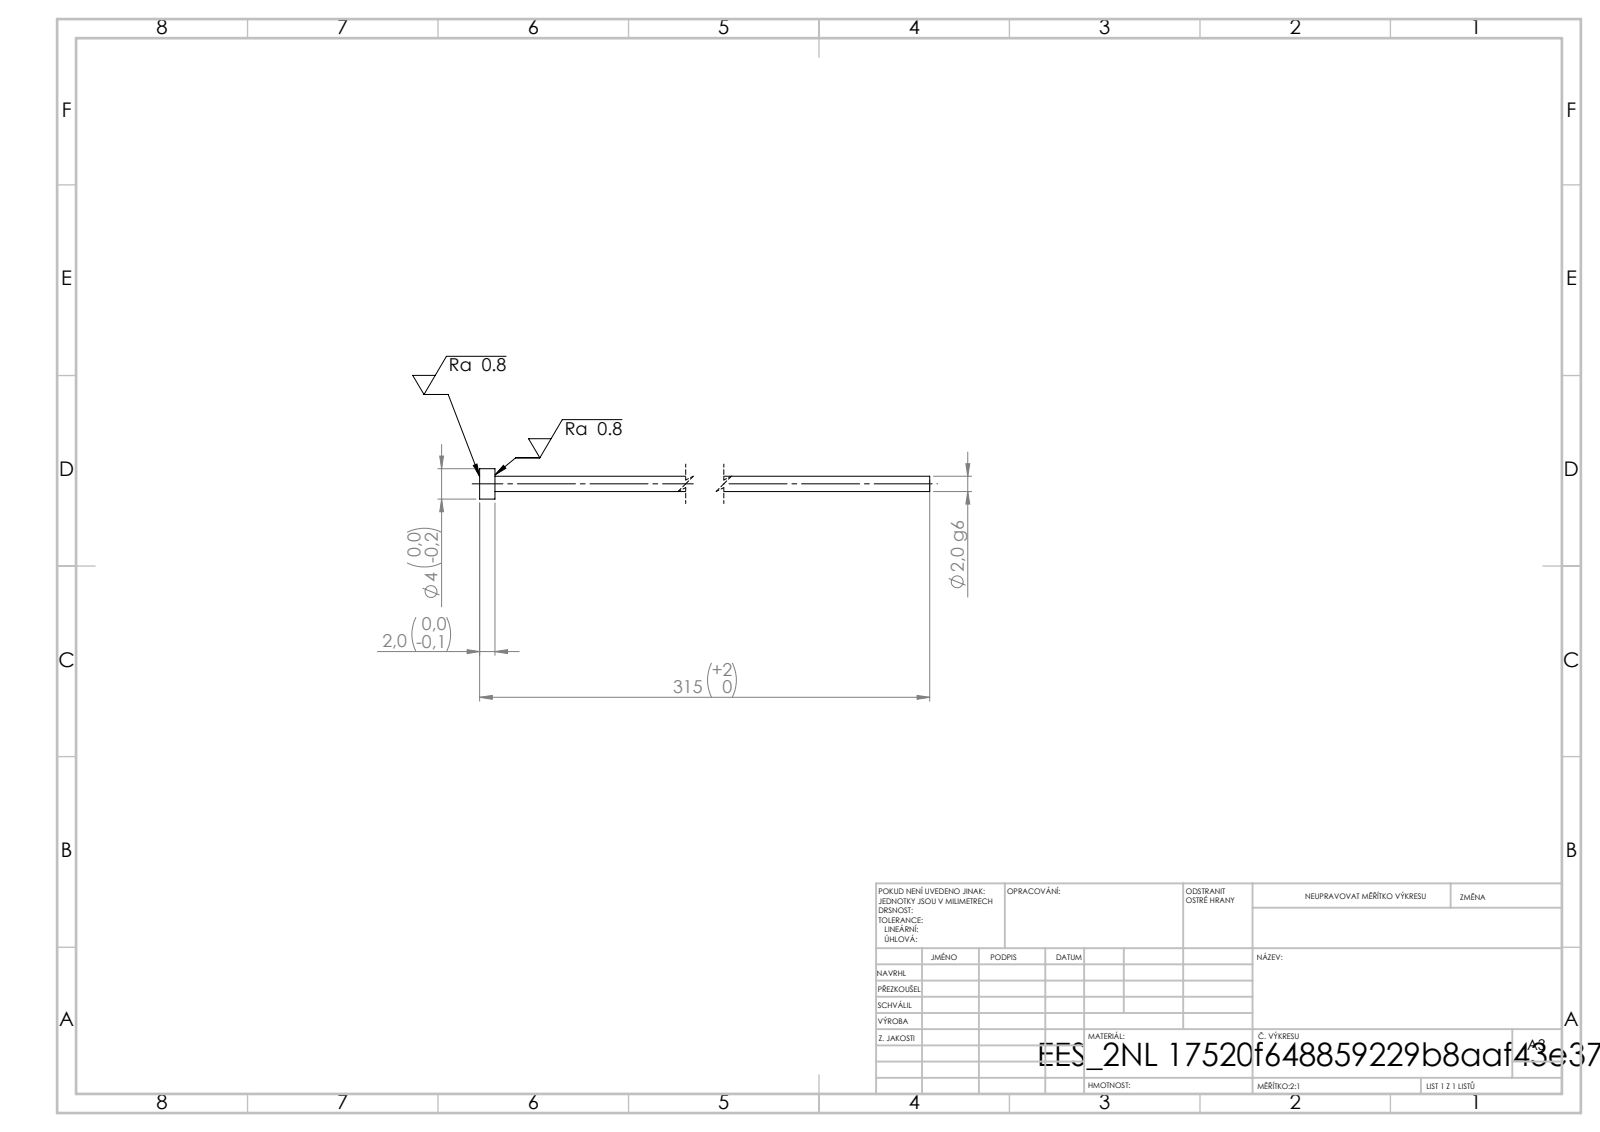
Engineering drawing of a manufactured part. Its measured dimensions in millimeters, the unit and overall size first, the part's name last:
Units: millimetres
Overall size (bounding box): 315 × 4 × 4
Round bosses / shafts (diameter × count): ⌀4 ×1, ⌀2 ×1
Main face-to-face distances: 2, 315, 313
Volume: 1 008 mm³ · Surface area: 2 017 mm²
Bodies: 1 solid, 7 faces (3 planar, 4 cylindrical, 0 other)
STEP written by: SolidWorks 2019 (CONFIG_CONTROL_DESIGN)
